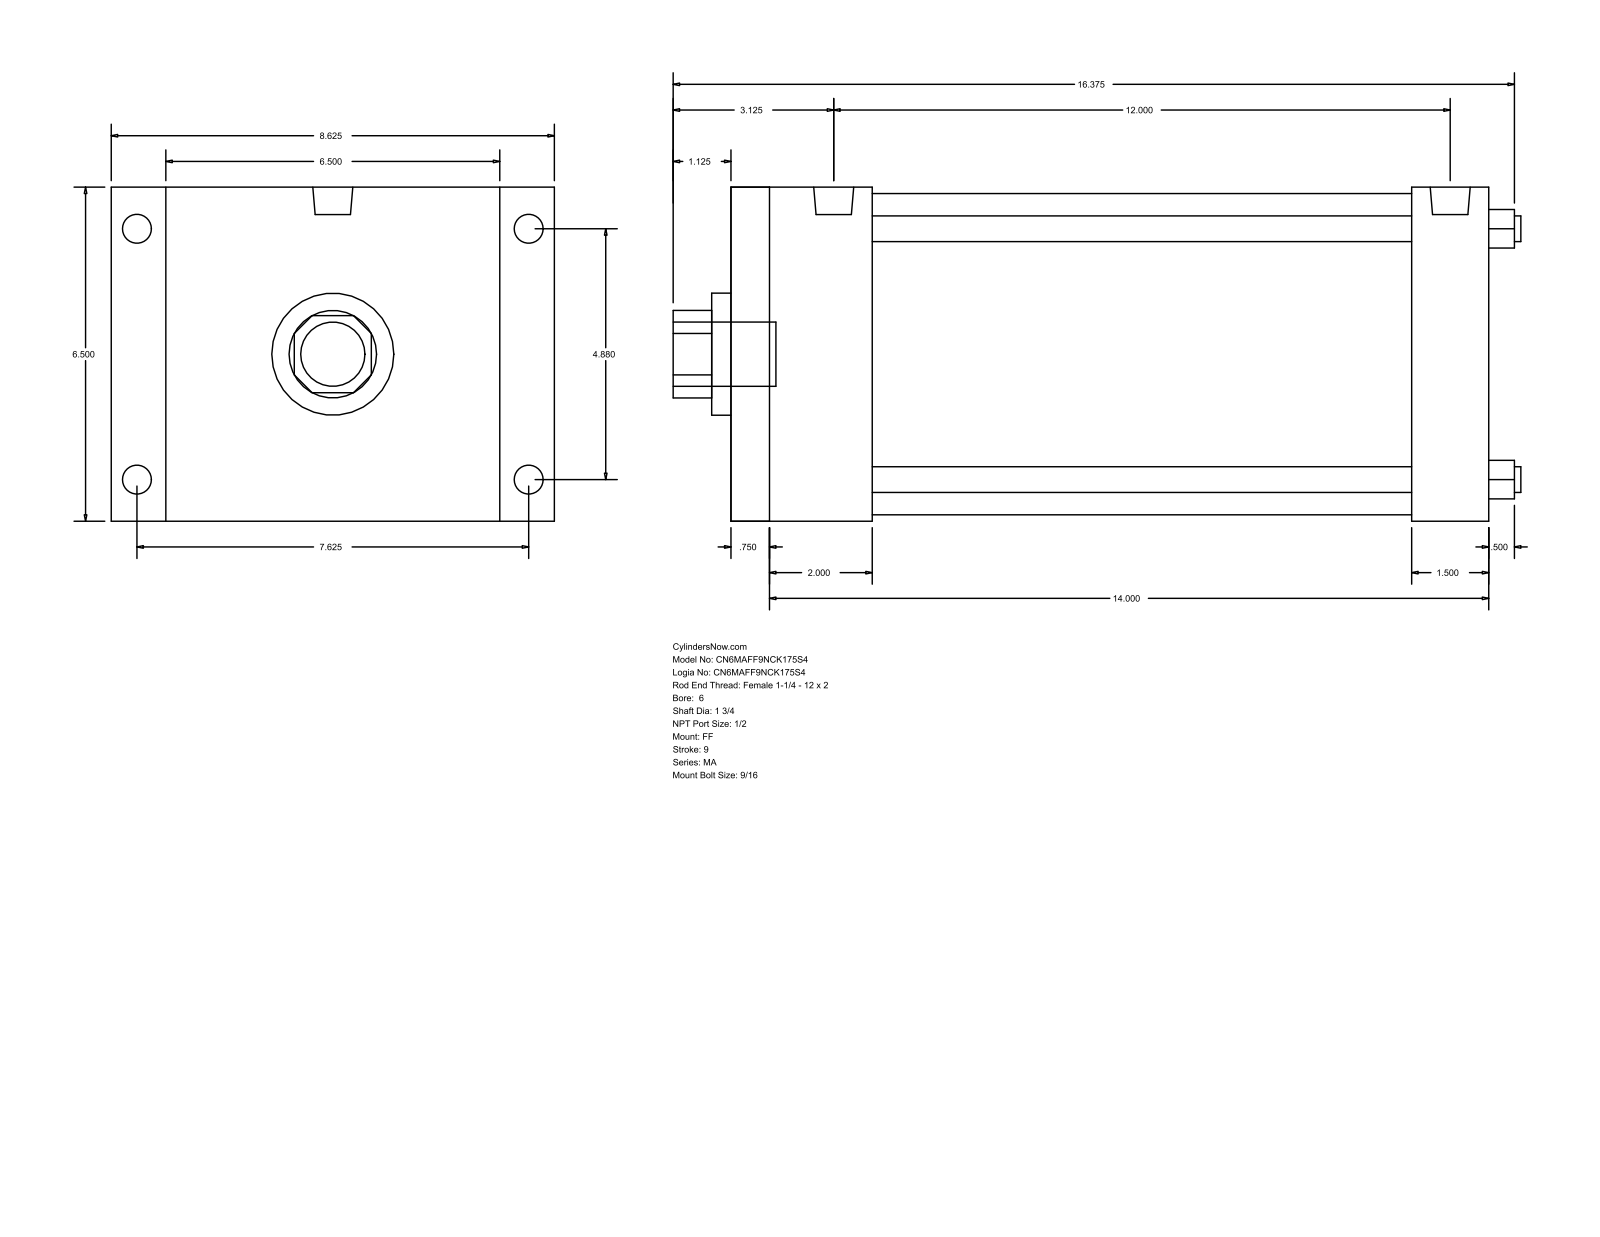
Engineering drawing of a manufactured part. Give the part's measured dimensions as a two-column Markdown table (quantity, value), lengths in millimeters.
| quantity | value |
| --- | --- |
| part name | MA_FF__0600_1.75 |
| STEP written by | GSSL Pune (CONFIG_CONTROL_DESIGN) |
| units | millimeters |
| bodies | 0 solids, 92 faces (64 planar, 28 cylindrical, 0 other) |
| overall size | 419.1 × 219.07 × 165.1 |
| round holes (diameter × count) | 12.7 × 4, 44.45 × 1, 60.33 × 1, 158.75 × 1 |
| round bosses / shafts (diameter × count) | 17.46 × 4, 14.29 × 4, 19.77 × 2, 31.75 × 1 |
| partial cylindrical surfaces (radius × count) | 21.63 × 1 |
| main face-to-face distances | 165.1, 374.66, 19.05, 355.61, 50.8, 69.85, 304.81, 336.55, 317.5, 266.7 |
| hole center spacings | 87.65, 123.96, 175.31 |
